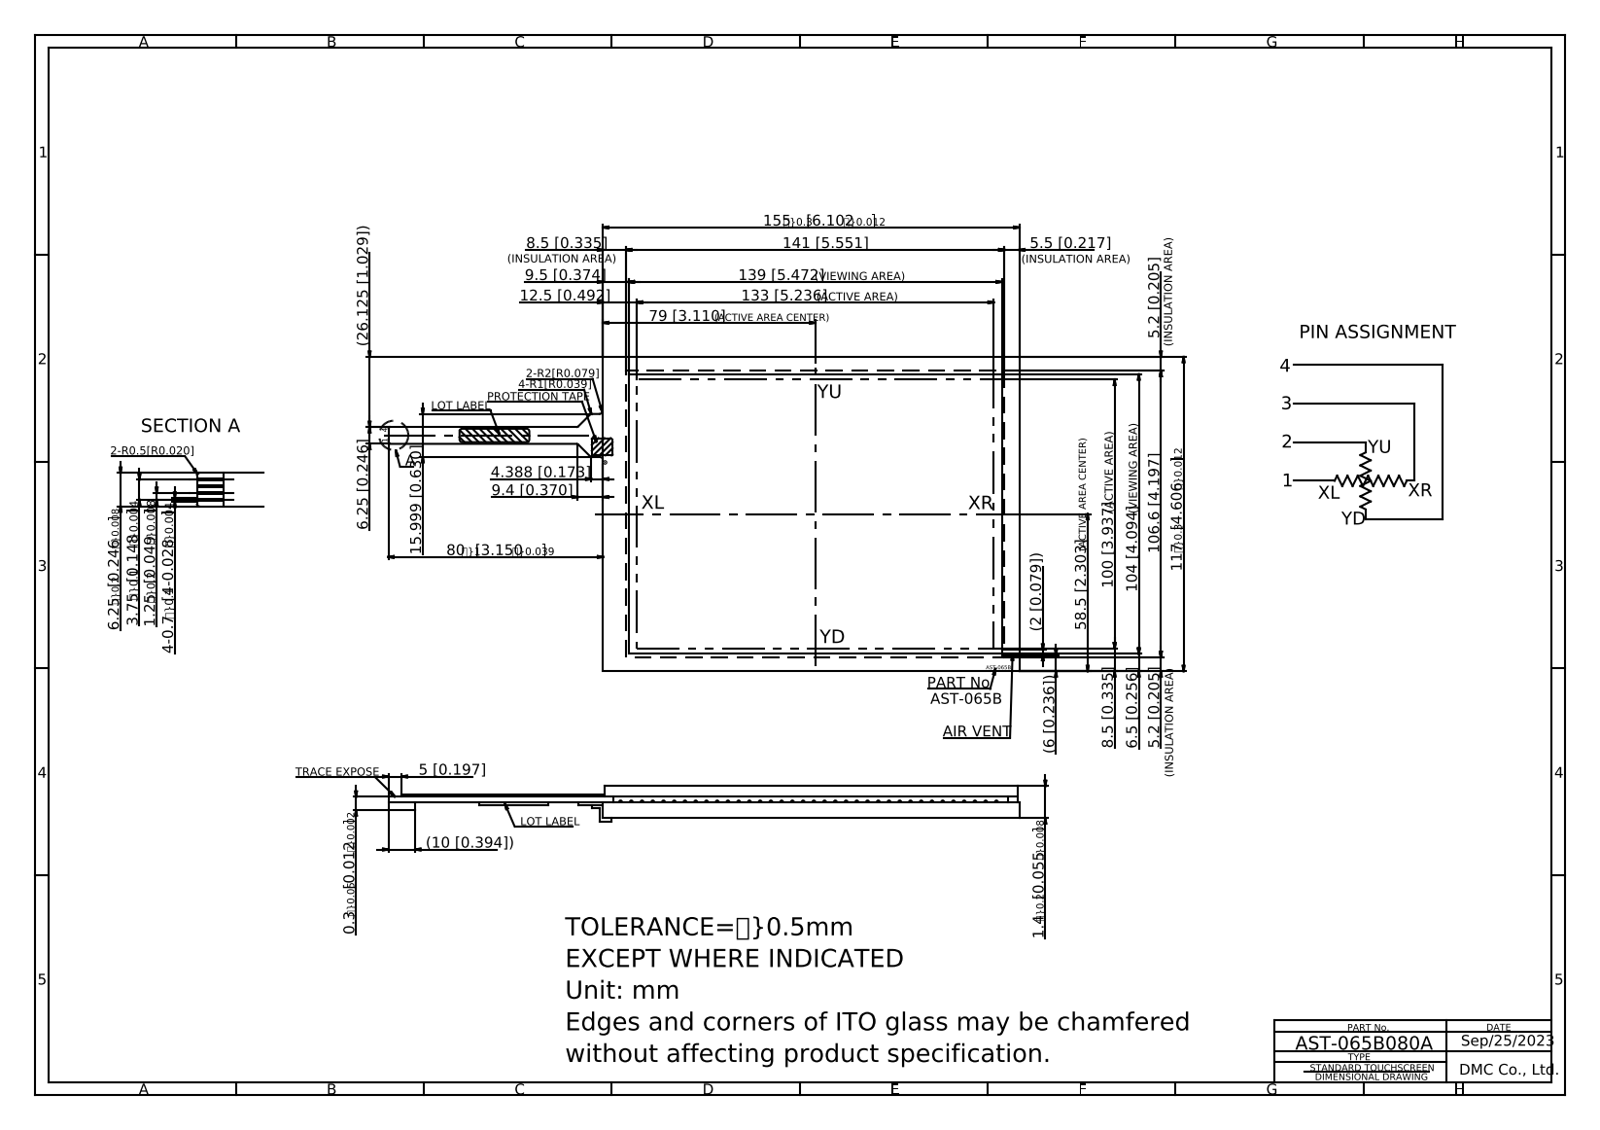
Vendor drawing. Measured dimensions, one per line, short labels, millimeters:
name: AST-065B080A
written by: Autodesk Inventor 2020 (CONFIG_CONTROL_DESIGN)
unit: mm
bodies: 1 solid, 51 faces (45 planar, 6 cylindrical, 0 other)
size: 266 × 163.8 × 1.4
volume: 25 345 mm³; area: 38 284 mm²
rounds: 4× R1, 2× R0.5
face distances: 1.4, 1.3, 1.2, 1.1, 117, 155, 0.8, 0.4, 0.5, 0.6
